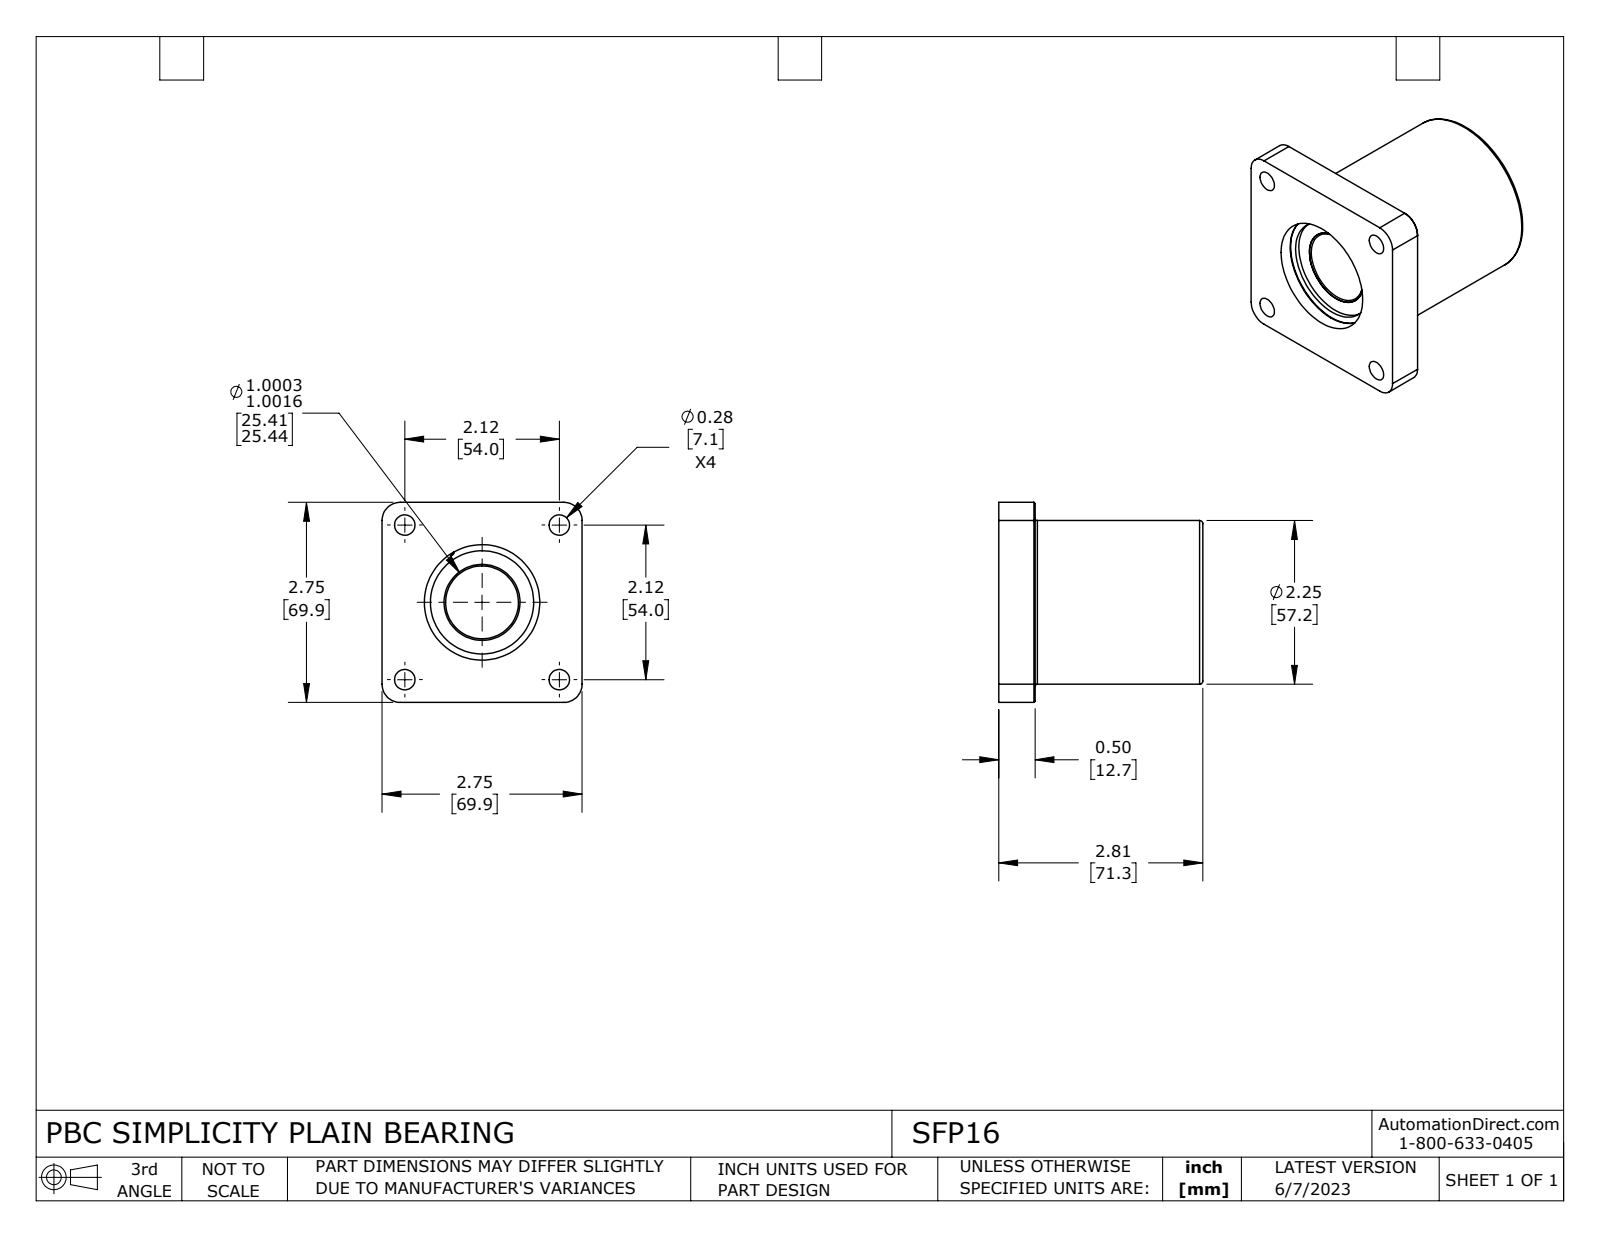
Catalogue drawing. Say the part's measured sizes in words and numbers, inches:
The part is named "SFP16". Its 3-D file was written by "SolidWorks 2021 (CONFIG_CONTROL_DESIGN)". It is 7 solids with 169 faces: 41 planar, 74 cylindrical and 54 other. Overall it measures 2.807 by 2.75 by 2.75 inches. Its volume is 9.813 cubic inches and its surface area 91.86 square inches. Round holes: 4 of diameter 0.281, 1 of diameter 1.001, 1 of diameter 1.045, 1 of diameter 1.419, 1 of diameter 1.587, 1 of diameter 1.658. Round bosses or shafts: 1 of diameter 2.25, 1 of diameter 1.675, 1 of diameter 1.562, 1 of diameter 1.471, 1 of diameter 1.399. Partial cylindrical surfaces (rounded edges, fillets, slot ends): 4 of radius 0.021, 4 of radius 0.25, 2 of radius 0.016, 2 of radius 0.026. The main face-to-face distances are 0.5, 2.75, 2.807, 2.307, 0.2, 2.607, 2.524, 2.024, 0.283, 0.282. The hole center spacings are 1.503, 2.125, 3.006.
